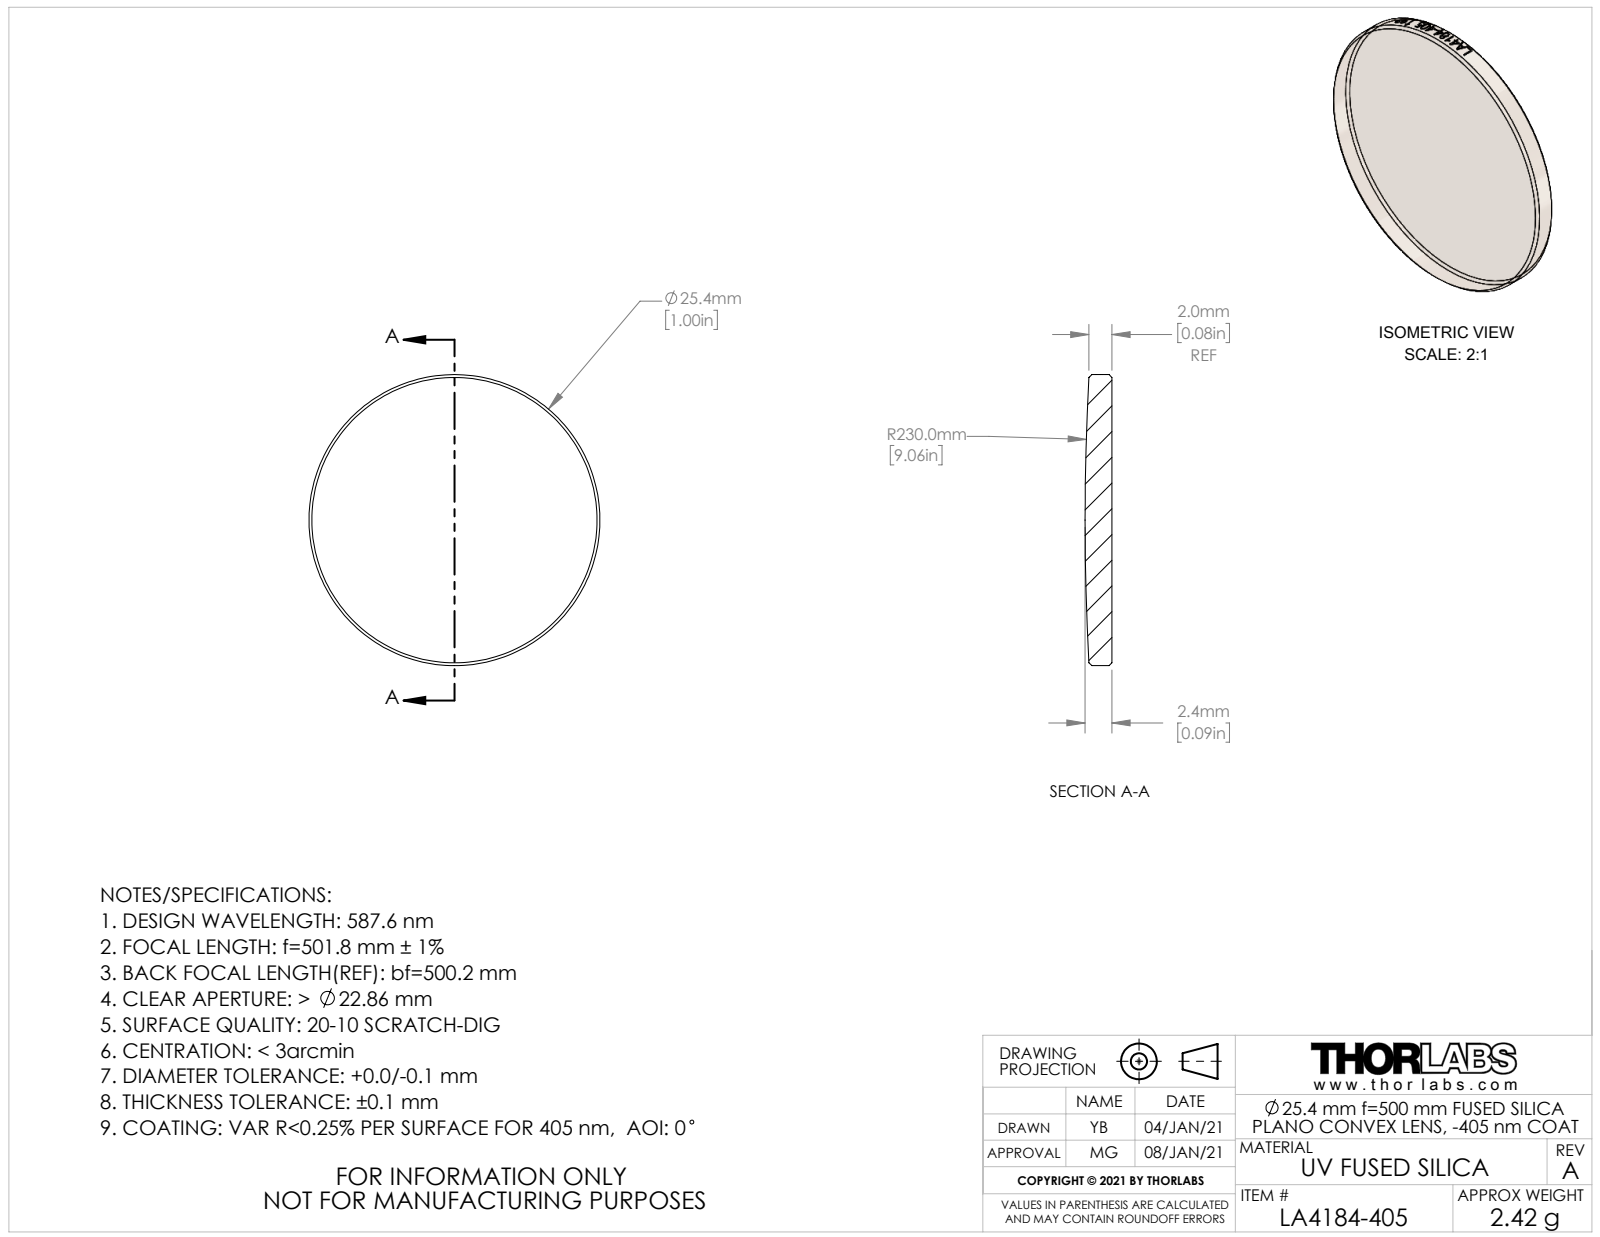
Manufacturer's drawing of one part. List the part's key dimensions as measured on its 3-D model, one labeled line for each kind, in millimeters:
Part name (STEP PRODUCT): CTN016823-E0W; CTN016843
STEP written by: SolidWorks 2018 (AUTOMOTIVE_DESIGN)
Units: millimetres
Bodies: 1 solid, 34 faces (1 planar, 27 cylindrical, 6 other)
Overall size (bounding box): 25.4 × 25.4 × 2.4
Volume: 1 100 mm³ · Surface area: 1 150 mm²
Round bosses / shafts (diameter × count): ⌀25.4 ×1
